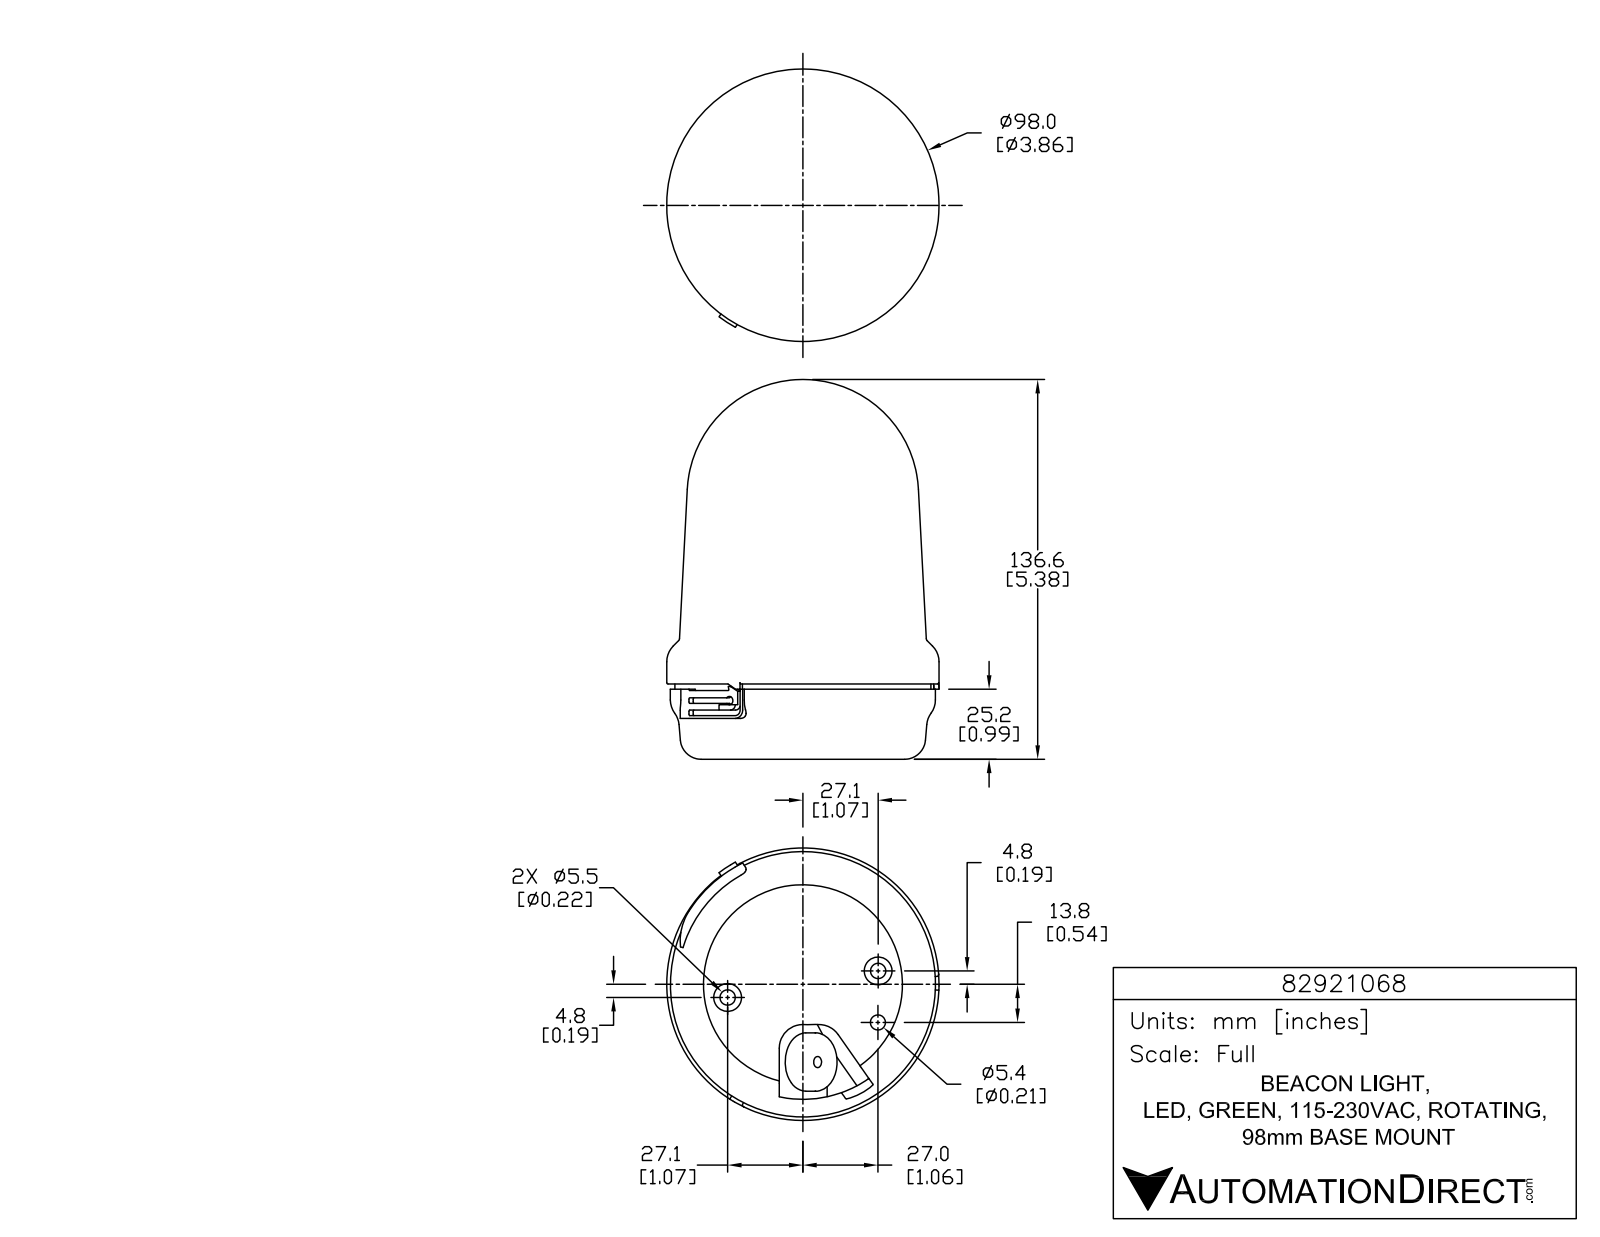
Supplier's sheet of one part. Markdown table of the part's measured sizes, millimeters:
| quantity | value |
| --- | --- |
| part name | 82921068 |
| STEP written by | SolidWorks 2015 (AUTOMOTIVE_DESIGN) |
| units | millimeters |
| bodies | 1 solid, 872 faces (566 planar, 204 cylindrical, 102 other) |
| overall size | 136.6 × 98 × 98 |
| volume | 732 300 mm³ |
| surface area | 47 520 mm² |
| round holes (diameter × count) | 1.5 × 3, 5.5 × 2, 4 × 1, 5.4 × 1, 71.6 × 1 |
| round bosses / shafts (diameter × count) | 8.6 × 3, 2.1 × 3, 10 × 2, 98 × 1, 95.4 × 1, 92.1 × 1, 21 × 1 |
| partial cylindrical surfaces (radius × count) | 0.1 × 9, 0.1 × 6, 0.3 × 6, 0.3 × 6, 0.3 × 6, 5 × 6, 0.5 × 5, 1 × 4 |
| main face-to-face distances | 26.5, 24.7, 1.9, 0.5, 25.2, 27.1, 6, 14.7, 14.2, 10.5 |
| hole center spacings | 27.5, 18.5, 30.3, 54.8, 55 |
